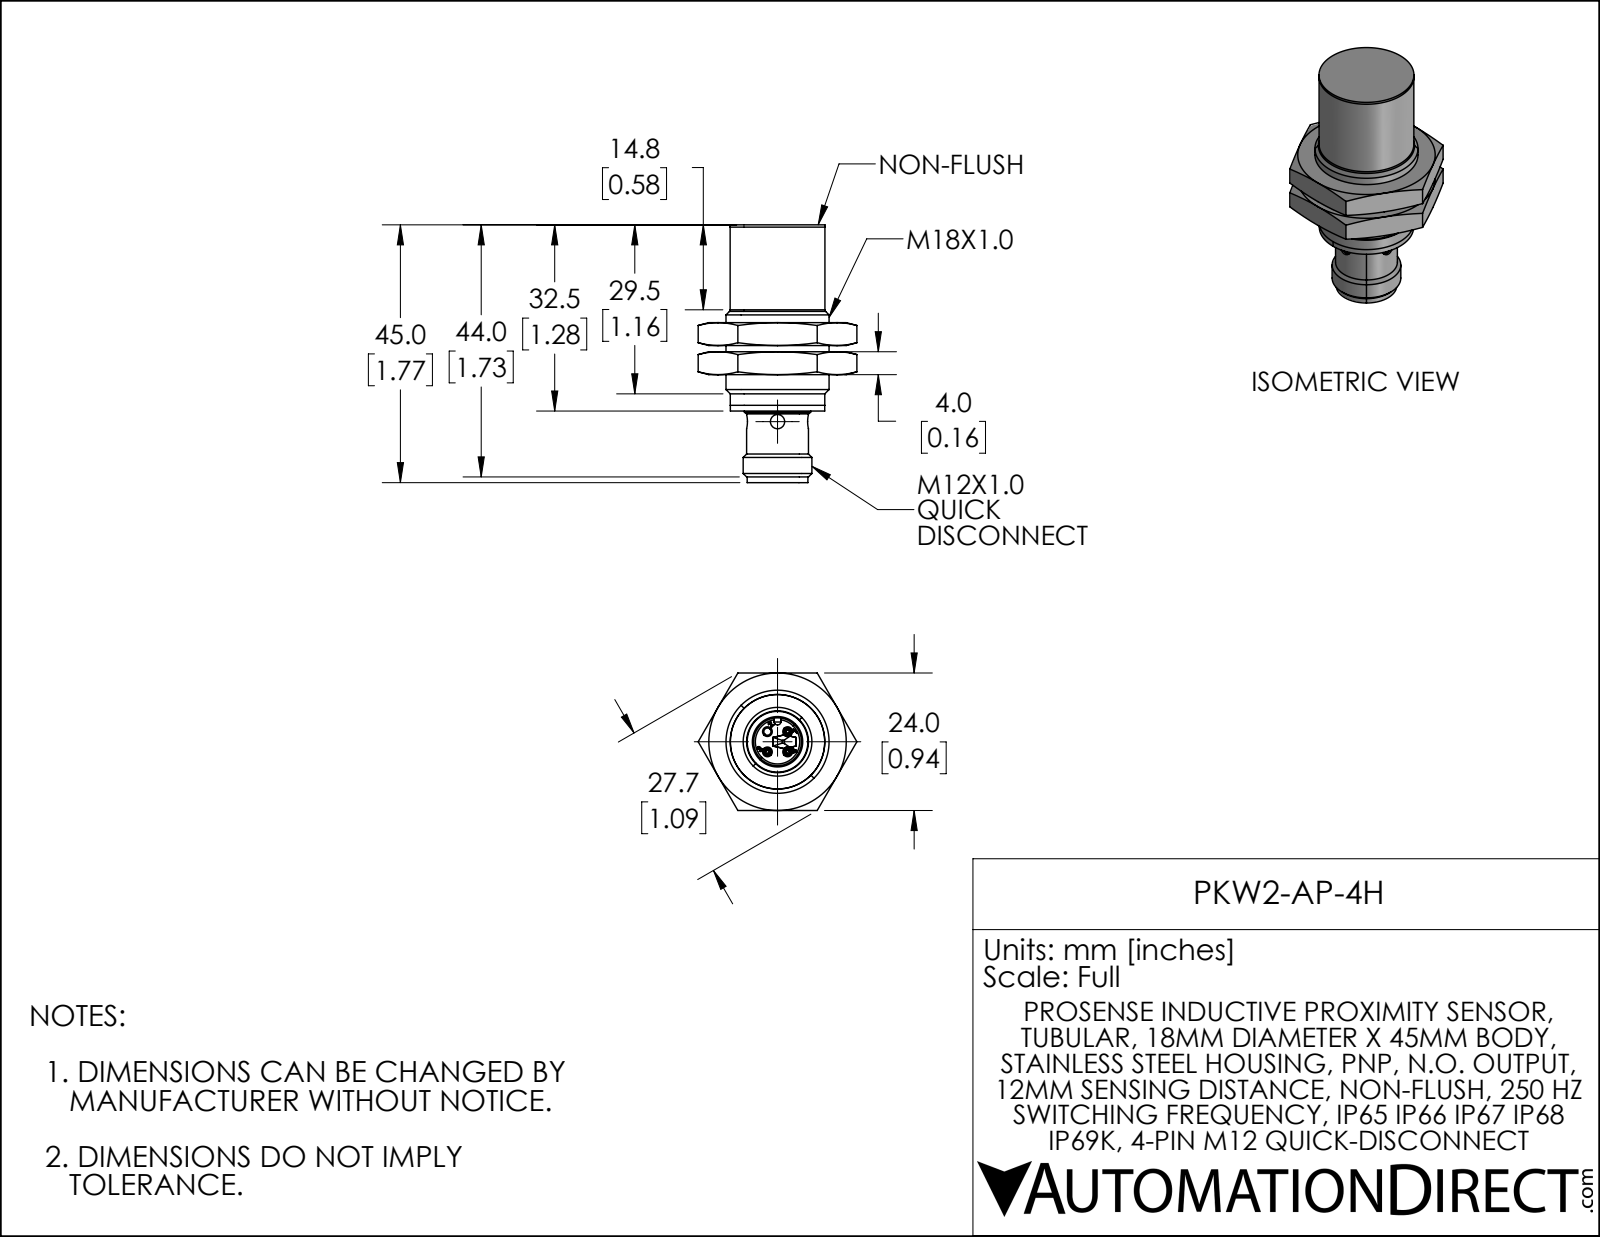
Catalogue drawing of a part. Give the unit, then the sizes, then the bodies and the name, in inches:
Units: inches
Overall size (bounding box): 1.772 × 1.091 × 0.945
Round holes (diameter × count): ⌀0.041 ×3, ⌀0.043 ×3, ⌀0.098 ×2, ⌀0.329 ×1, ⌀0.394 ×1, ⌀0.666 ×1
Round bosses / shafts (diameter × count): ⌀0.039 ×3, ⌀0.709 ×1, ⌀0.653 ×1, ⌀0.652 ×1, ⌀0.65 ×1, ⌀0.649 ×1, ⌀0.472 ×1, ⌀0.457 ×1
Partial cylindrical surfaces — rounded edges, fillets, slot ends (radius × count): R0.012 ×18, R0.02 ×3, R0.02 ×2, R0.02 ×1, R0.021 ×1, R0.024 ×1
Main face-to-face distances: 0.157, 0.2, 0.945, 0.672, 0.872, 0.83, 0.043, 1.03, 0.357, 0.407
Hole centre spacings: 0.098, 0.139, 0.197
Volume: 0.633 in³ · Surface area: 8.965 in²
Bodies: 3 solids, 378 faces (104 planar, 97 cylindrical, 177 other)
Part name (STEP PRODUCT): PKW2-AP-4H
STEP written by: SolidWorks 2019 (CONFIG_CONTROL_DESIGN)
